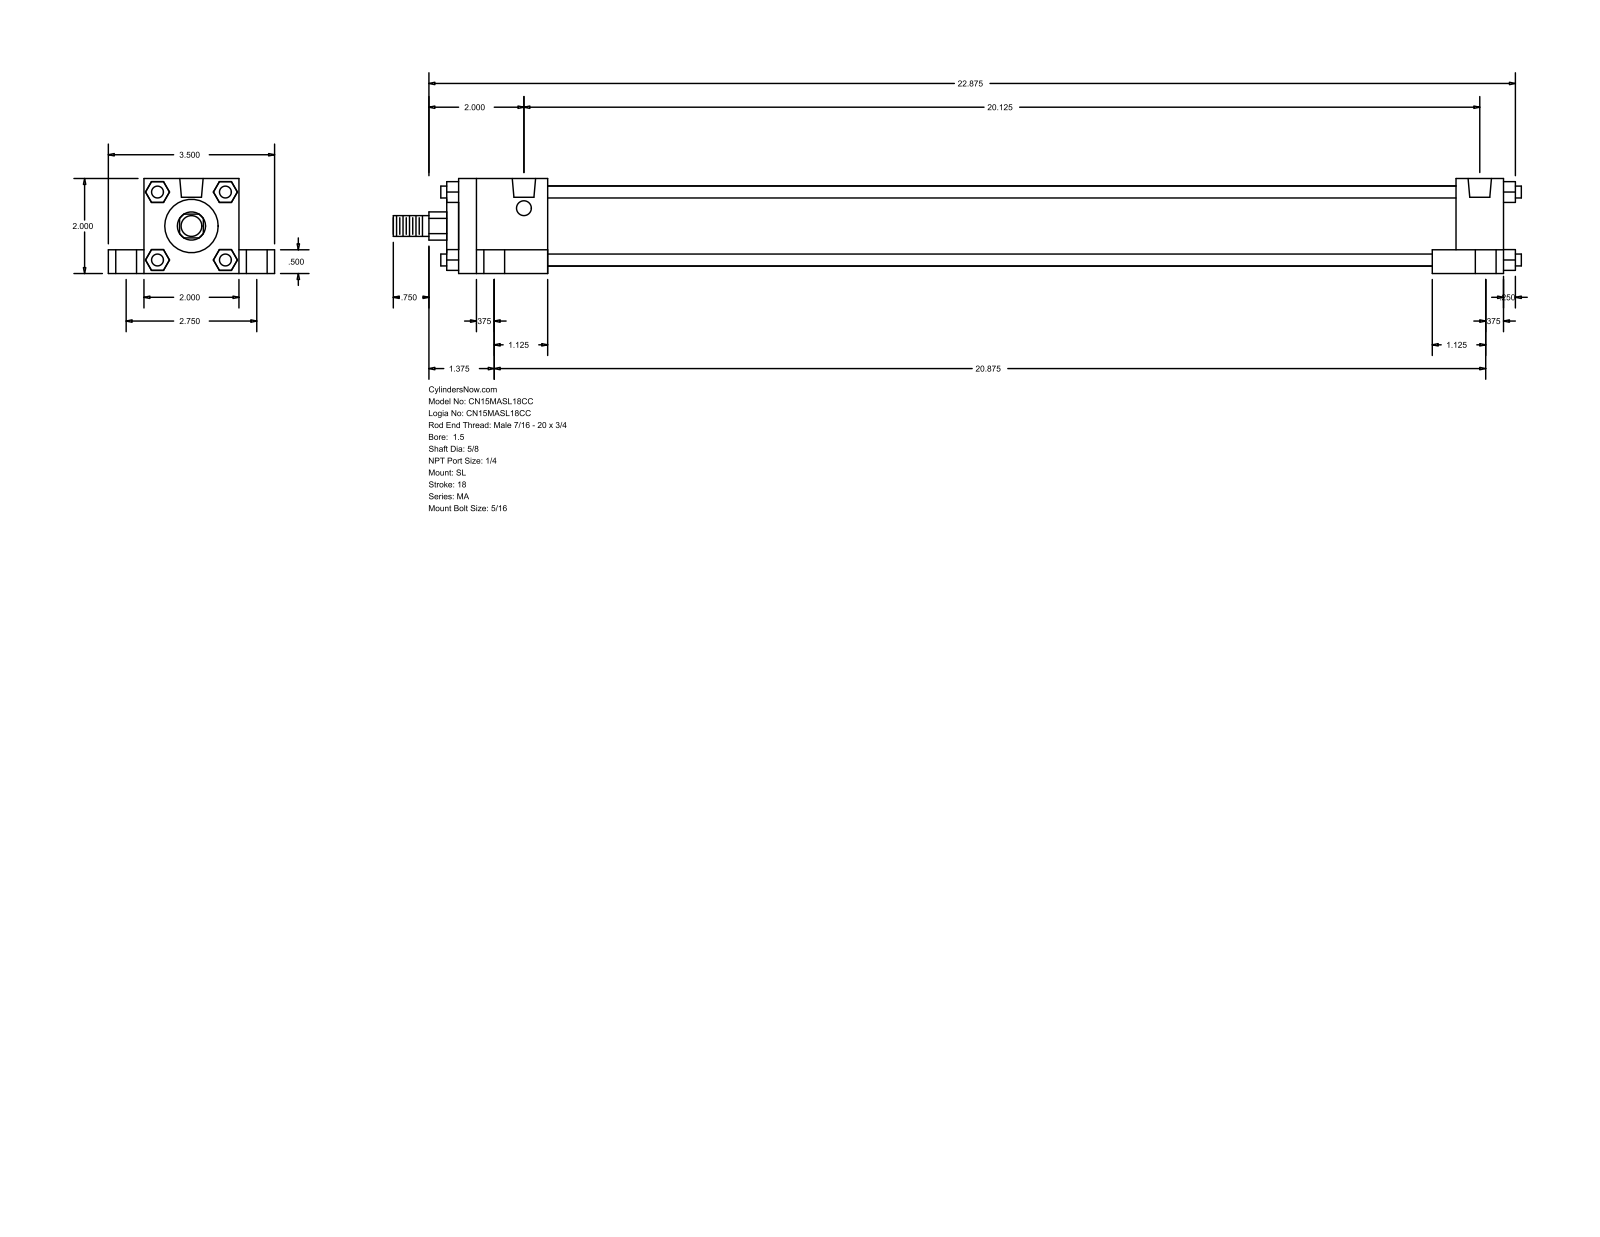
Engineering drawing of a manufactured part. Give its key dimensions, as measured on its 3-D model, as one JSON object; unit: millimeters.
{"part_name": "MA_SL__0150_0.625", "step_written_by": "GSSL Pune (CONFIG_CONTROL_DESIGN)", "units": "millimeters", "bodies": {"solids": 0, "faces": 148, "planar": 112, "cylindrical": 36, "other": 0}, "overall_size": [603.25, 88.9, 50.8], "round_holes": [[7.94, 4], [11.11, 4], [17.46, 4], [12.49, 2]], "round_bosses_or_shafts": [[6.35, 4], [42.93, 1], [28.57, 1], [15.88, 1], [11.11, 1]], "partial_cylinders_radius": [[7.54, 1]], "face_to_face_distances": [50.8, 19.05, 38.1, 69.85, 12.7, 558.79, 485.77, 25.4, 6.35, 9.52], "hole_center_spacings": [35.06, 38.36, 69.84, 511.18, 515.53, 528.22, 530.23, 534.81]}
